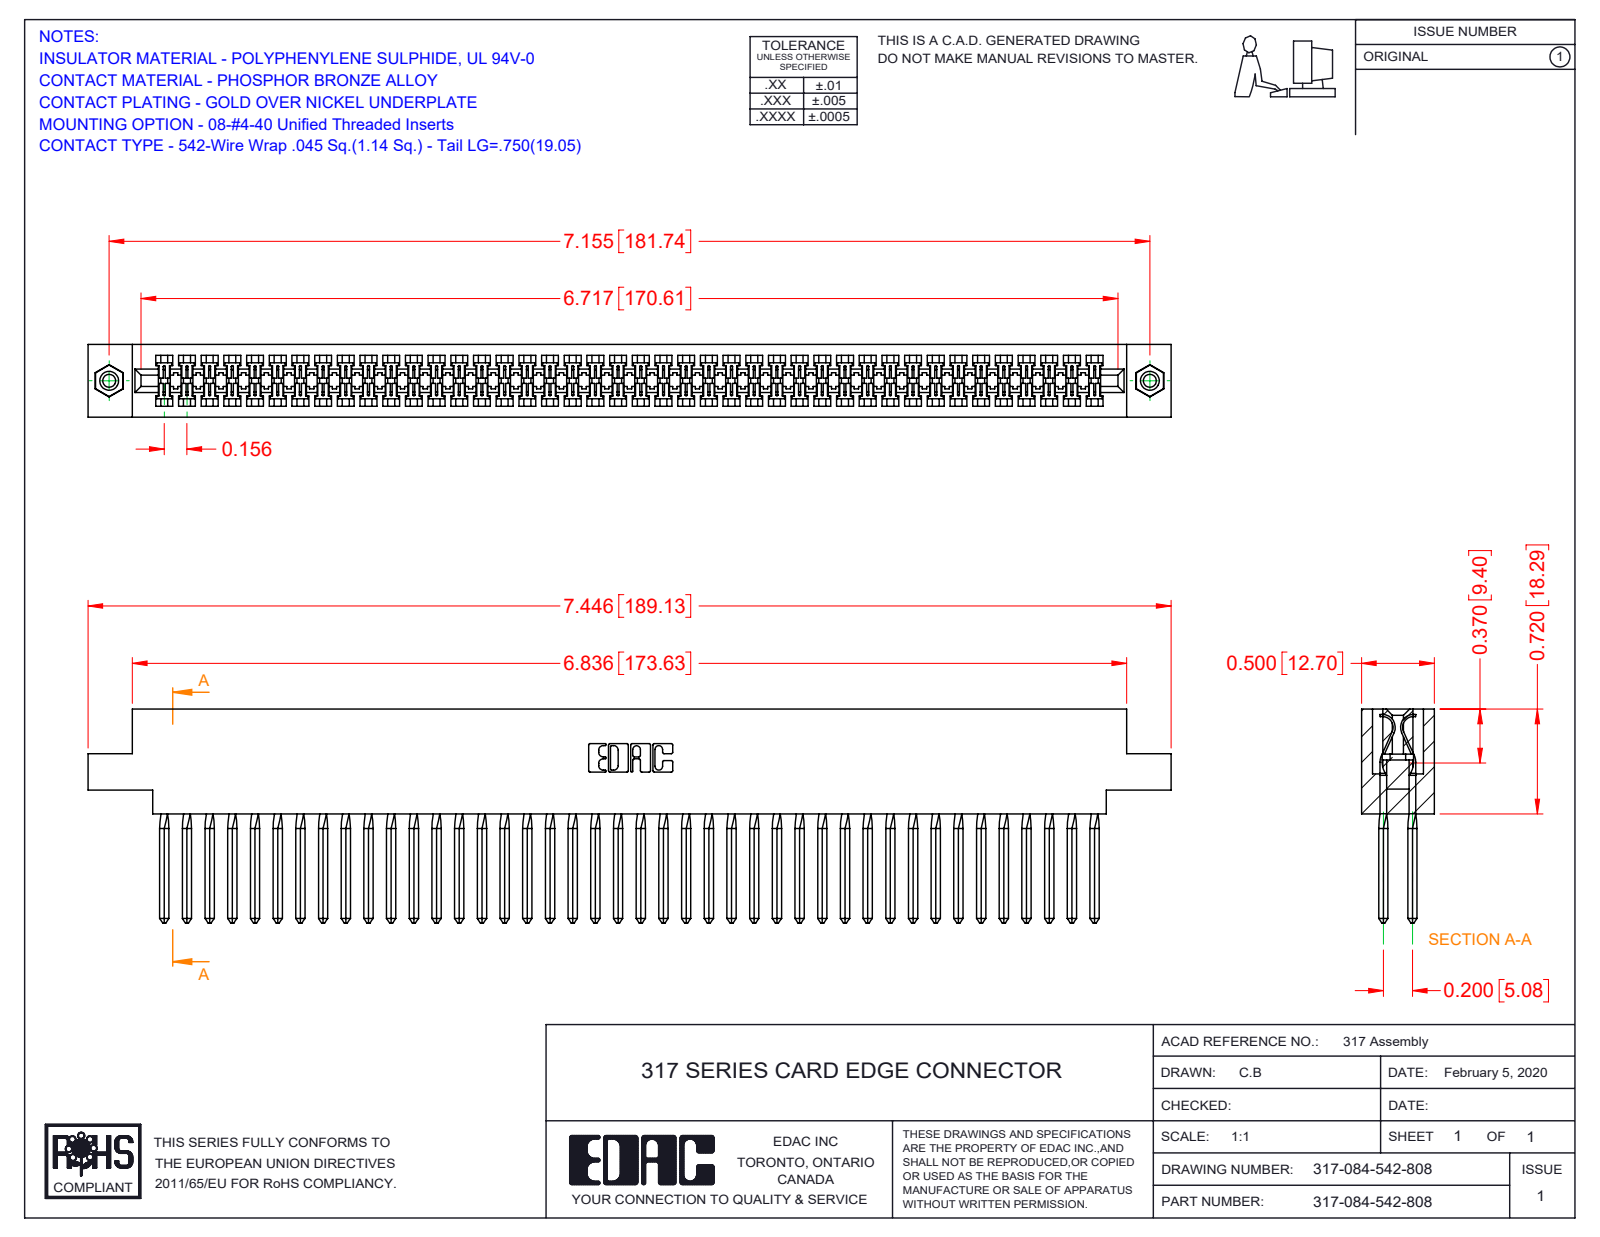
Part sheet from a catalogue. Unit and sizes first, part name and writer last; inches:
Units: inches
Overall size (bounding box): 7.446 × 1.47 × 0.5
Round holes (diameter × count): ⌀0.089 ×2, ⌀0.125 ×2, ⌀0.156 ×2
Round bosses / shafts (diameter × count): ⌀0.155 ×2
Partial cylindrical surfaces — rounded edges, fillets, slot ends (radius × count): R0.006 ×168, R0.01 ×22, R0.007 ×6, R0.031 ×6, R0.026 ×3, R0.074 ×2, R0.089 ×2, R0.1 ×2
Main face-to-face distances: 0.5, 0.075, 0.425, 0.35, 0.2, 0.046, 0.128, 0.372, 0.052, 0.297
Hole centre spacings: 7.155
Volume: 1.889 in³ · Surface area: 66.77 in²
Bodies: 87 solids, 4950 faces (3954 planar, 644 cylindrical, 352 other)
Part name (STEP PRODUCT): 345-250-001_345-250-003-102; 317 Part_.156 Dia - TI; 317-084-542-808; 317-290-003_542
STEP written by: SolidWorks 2016 (CONFIG_CONTROL_DESIGN)
